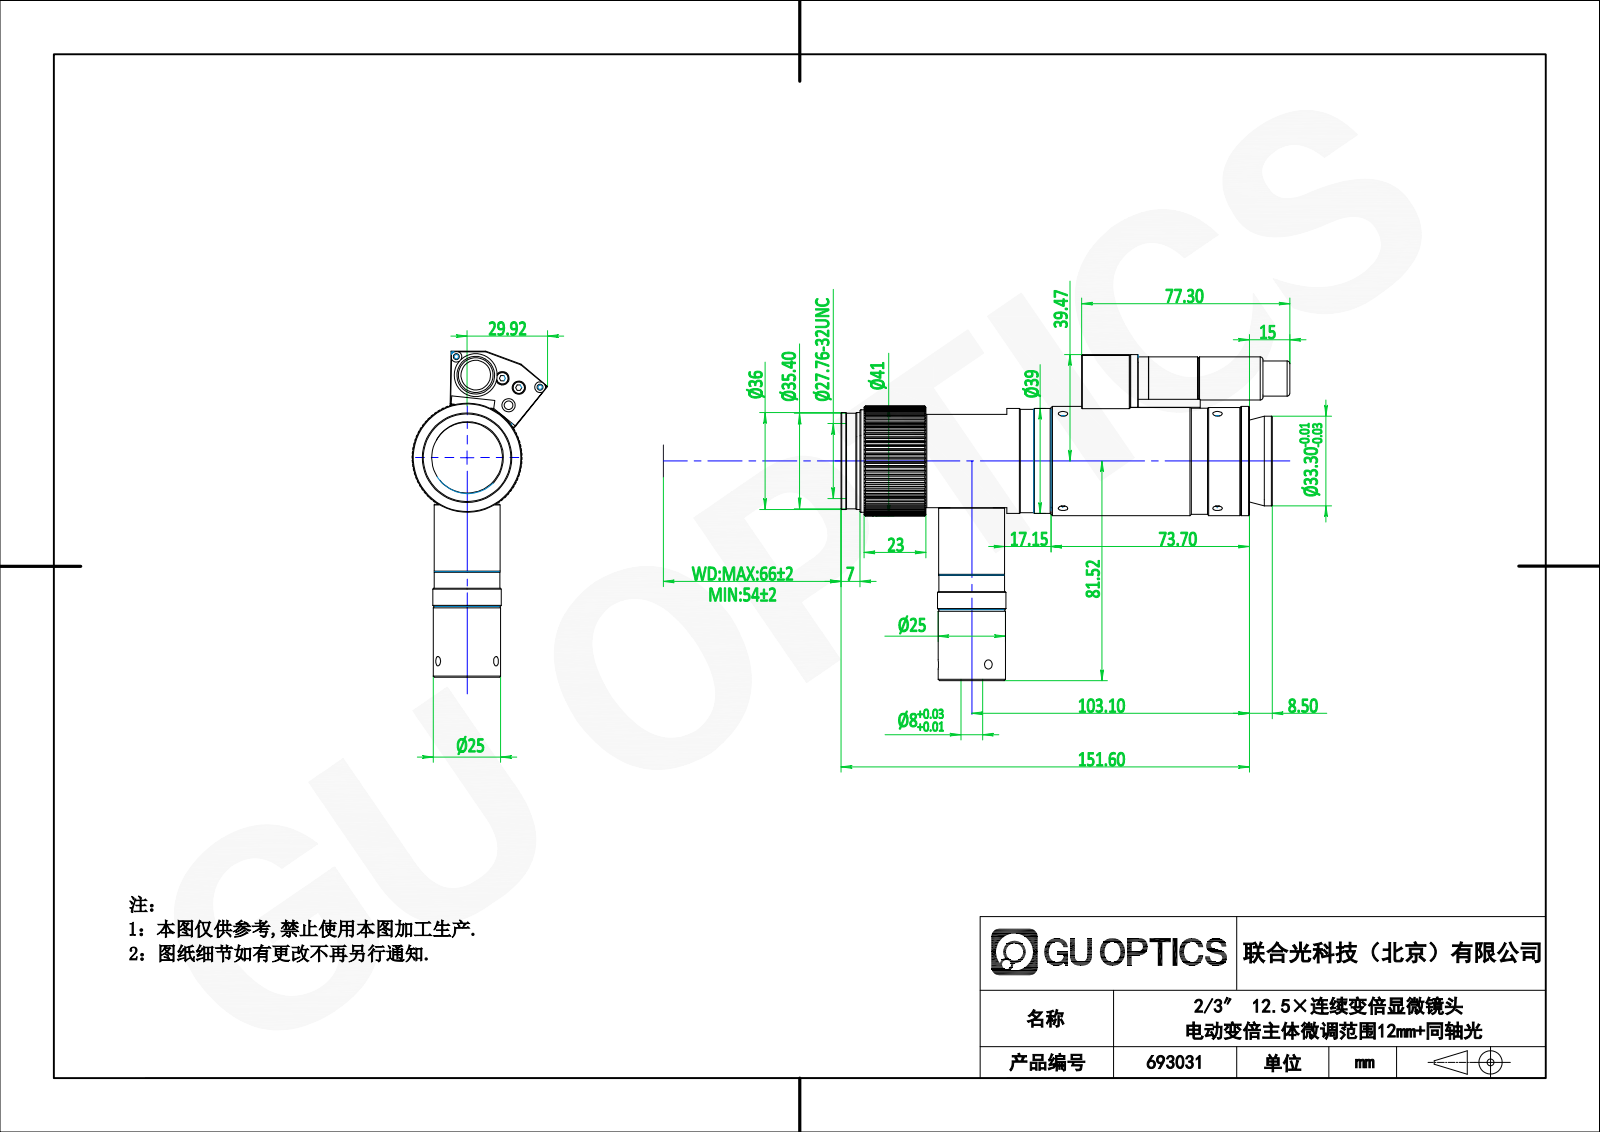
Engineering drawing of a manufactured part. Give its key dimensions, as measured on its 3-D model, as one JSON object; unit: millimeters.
{"part_name": "693031", "step_written_by": "SolidWorks 2020 (CONFIG_CONTROL_DESIGN)", "units": "millimeters", "bodies": {"solids": 0, "faces": 471, "planar": 292, "cylindrical": 131, "other": 48}, "overall_size": [166.6, 121, 50.32], "round_holes": [[5, 7], [3.5, 3], [2.3, 2], [1.6, 1], [3.3, 1], [8, 1], [35.4, 1], [36, 1], [38, 1], [39.6, 1], [40.6, 1]], "round_bosses_or_shafts": [[3.5, 5], [4.5, 2], [39, 1], [38.4, 1], [34.8, 1], [34, 1], [33.3, 1], [31.5, 1]], "partial_cylinders_radius": [[20.4, 1]], "face_to_face_distances": [3, 41, 59, 18, 2, 3.3, 44.3, 62.3, 60.3, 57], "hole_center_spacings": [8, 10, 12.81, 37.69, 7, 7.5, 7.96, 10.26]}
